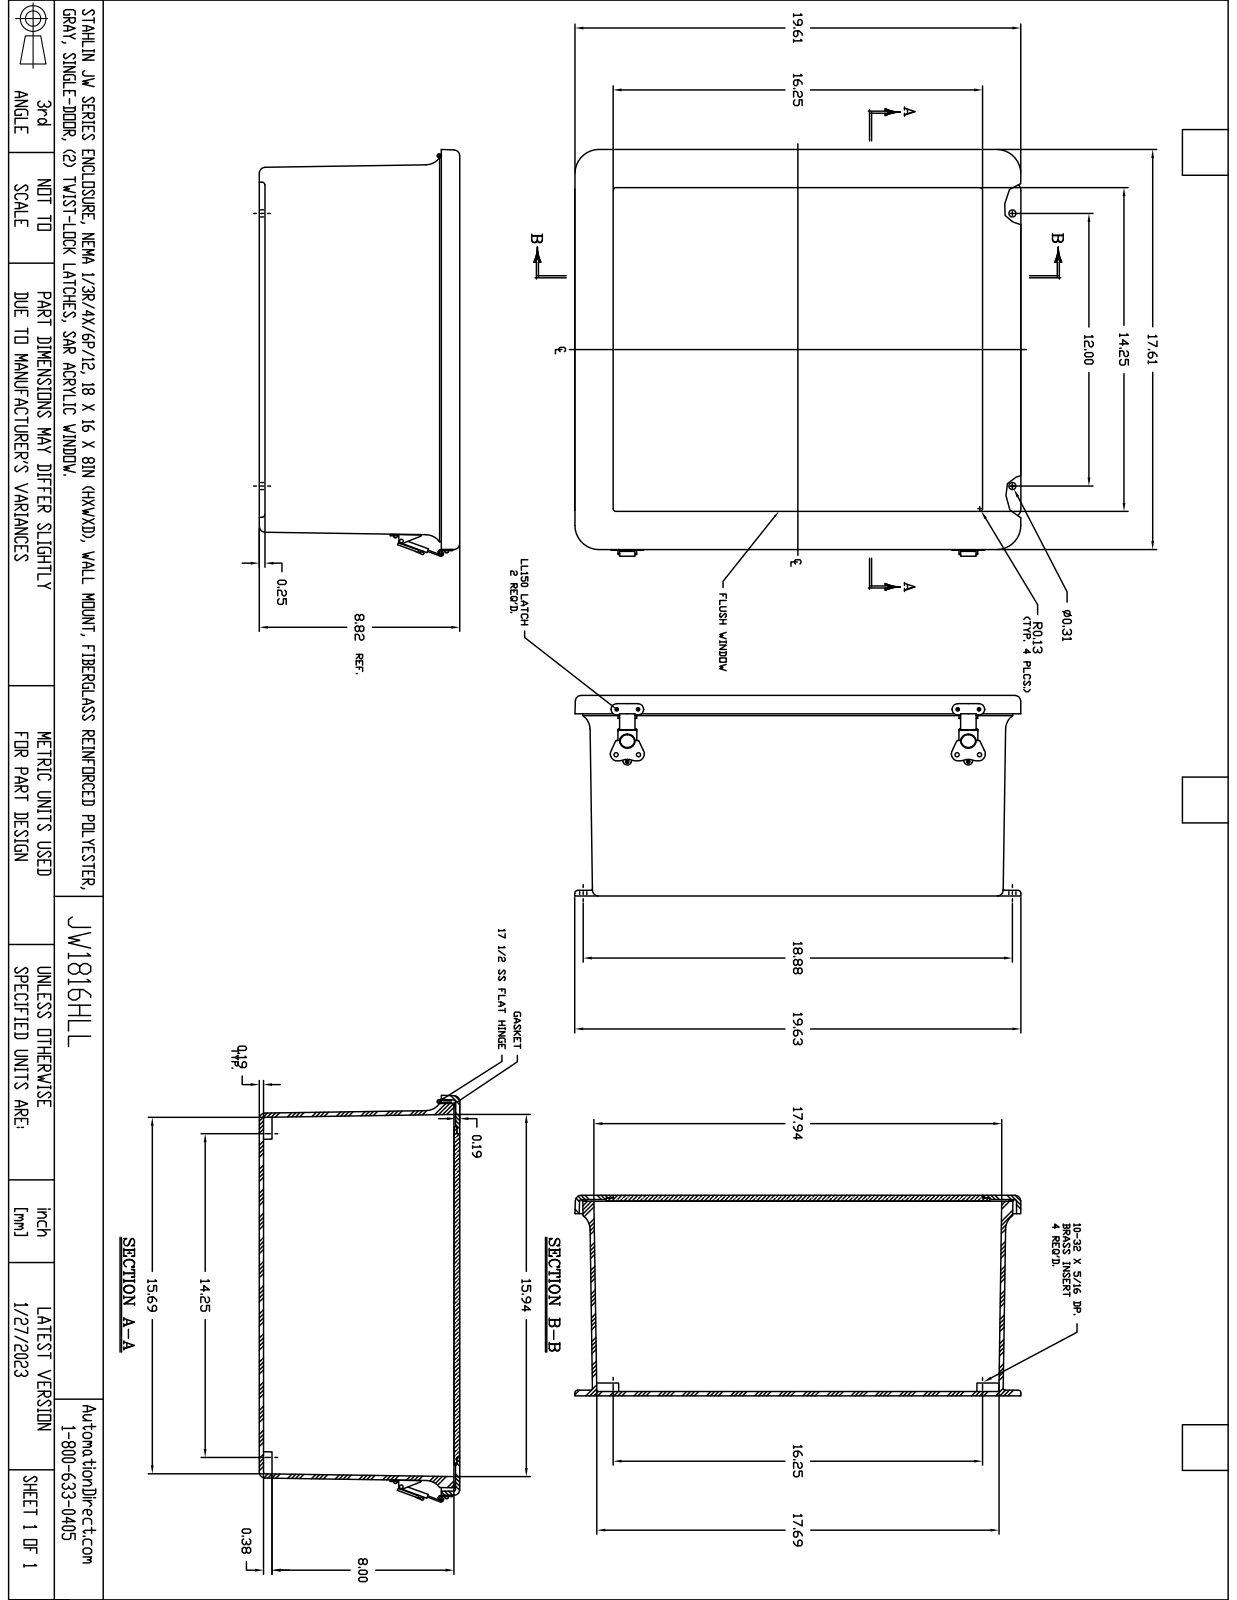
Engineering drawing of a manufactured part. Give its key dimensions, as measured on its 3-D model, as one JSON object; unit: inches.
{"part_name": "MW1816HLL", "step_written_by": "SolidWorks 2018 (AUTOMOTIVE_DESIGN)", "units": "inches", "bodies": {"solids": 53, "faces": 1322, "planar": 610, "cylindrical": 517, "other": 195}, "overall_size": [19.625, 17.917, 8.812], "volume_in3": 275.9, "surface_area_in2": 2794, "round_holes": [[0.14, 20], [0.131, 12], [0.152, 5], [0.13, 4], [0.156, 4], [0.165, 4], [0.197, 4], [0.218, 4], [0.118, 2], [0.138, 2], [0.181, 2], [0.182, 2]], "round_bosses_or_shafts": [[0.25, 20], [0.125, 11], [0.125, 9], [0.27, 4], [0.583, 2], [0.524, 2], [0.209, 2], [0.185, 2]], "partial_cylinders_radius": [[0.031, 20], [0.079, 19], [0.125, 16], [0.25, 12], [0.037, 8], [0.039, 8], [0.045, 8], [0.047, 8]], "face_to_face_distances": [0.187, 8.812, 0.188, 0.25, 8.562, 8.624, 8.374, 8.624, 8.437, 0.063], "hole_center_spacings": [14.984, 3.375, 3.375, 6.75, 0.25, 0.826, 14.984, 10.25]}
